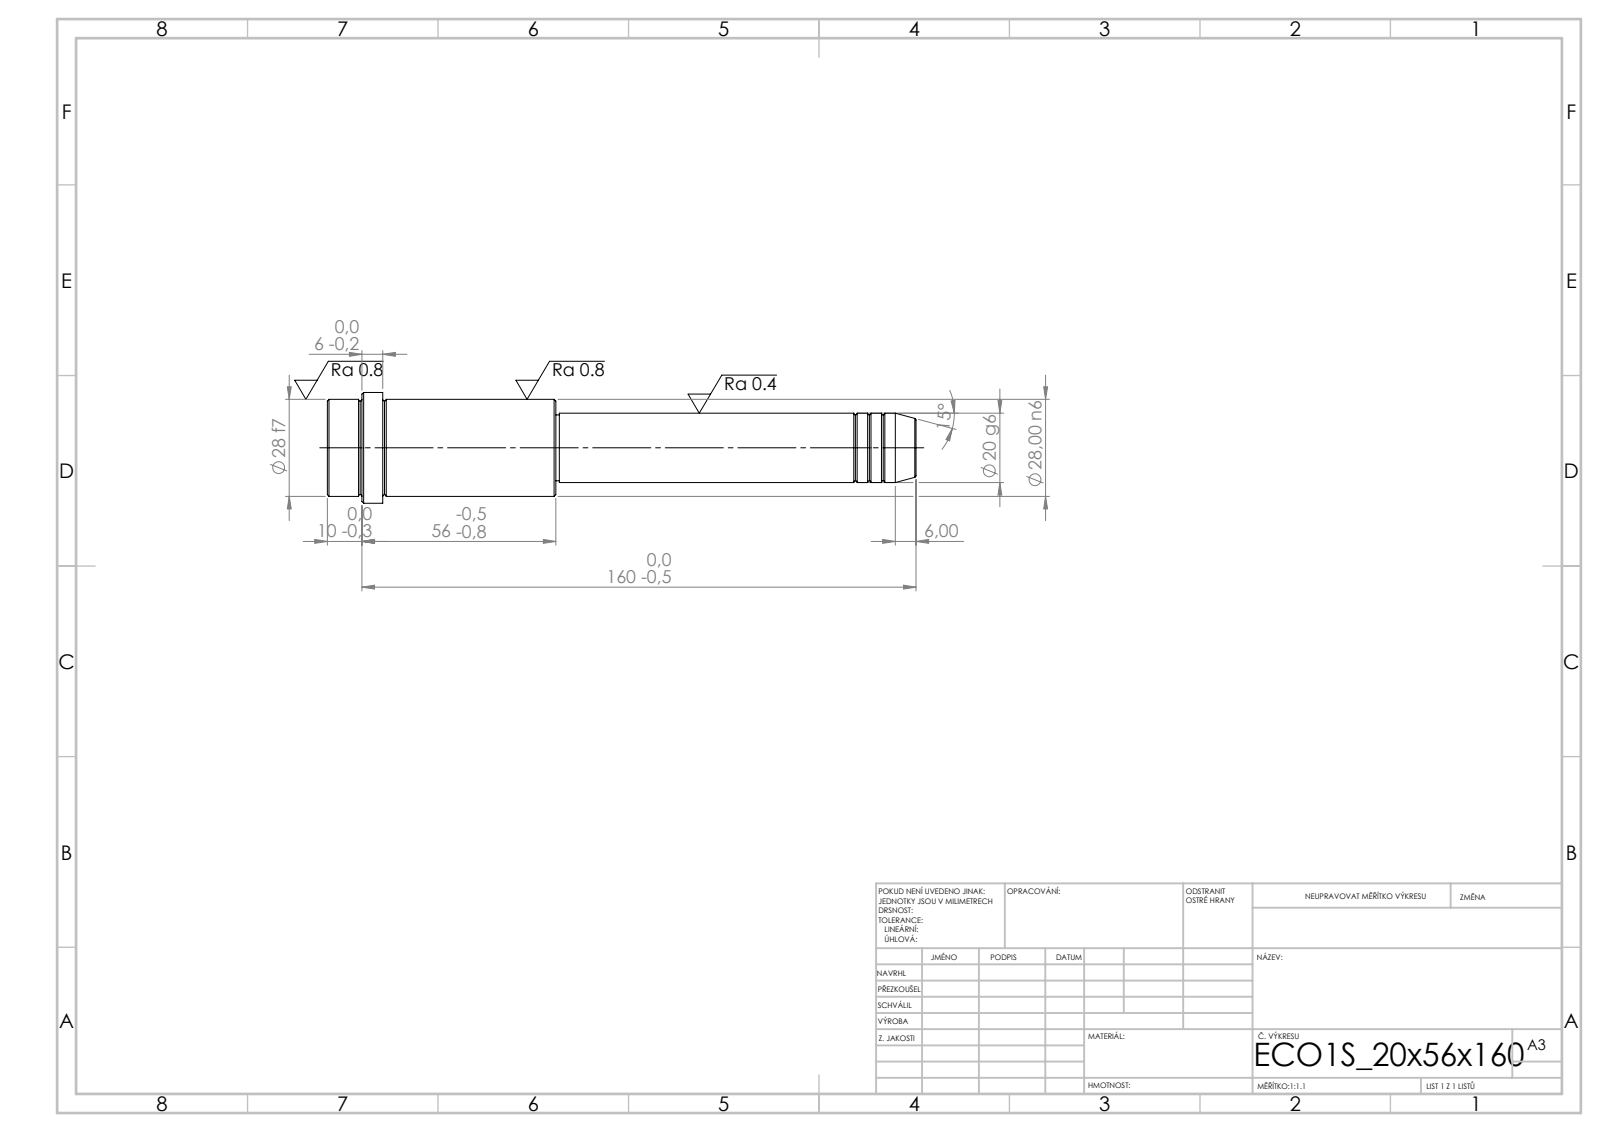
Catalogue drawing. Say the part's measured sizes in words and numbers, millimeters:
Its 3-D file was written by "SolidWorks 2019 (CONFIG_CONTROL_DESIGN)". It is 1 solid with 52 faces: 6 planar, 16 cylindrical and 30 other. Overall it measures 170 by 32 by 32 millimeters. Its volume is 73 950 cubic millimeters and its surface area 14 076 square millimeters. Round bosses or shafts: 1 of diameter 32, 1 of diameter 28, 1 of diameter 20, 1 of diameter 19. The main face-to-face distances are 66, 104, 170, 154, 50, 16, 160, 56, 6, 10.
